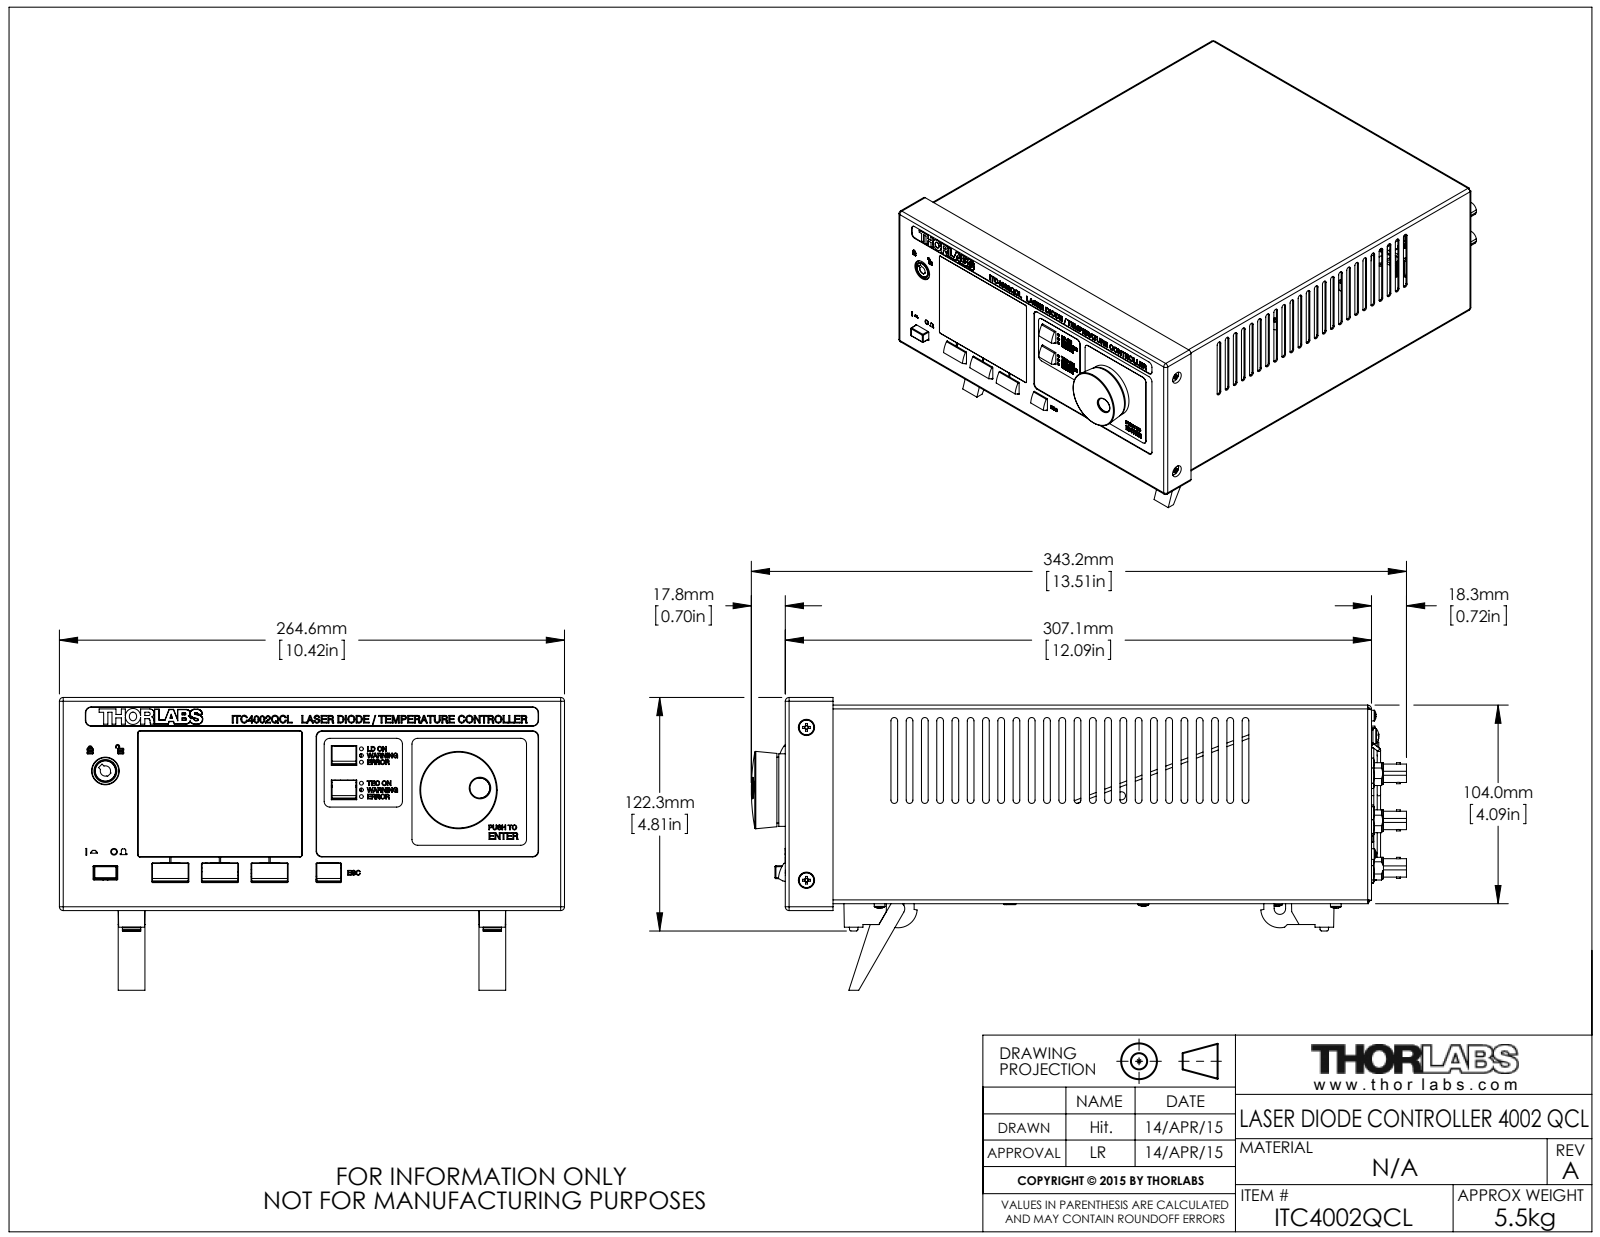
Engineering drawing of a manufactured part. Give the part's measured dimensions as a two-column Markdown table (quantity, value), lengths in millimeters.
| quantity | value |
| --- | --- |
| part name | MTN004957-E0W |
| STEP written by | SolidWorks 2014 (AUTOMOTIVE_DESIGN) |
| units | millimeters |
| bodies | 113 solids, 14390 faces (8699 planar, 2452 cylindrical, 3239 other) |
| overall size | 343.22 × 264.6 × 153.33 |
| volume | 734 865 mm³ |
| surface area | 897 095 mm² |
| round holes (diameter × count) | 2.5 × 37, 5.4 × 27, 1 × 25, 1.1 × 25, 3 × 18, 5.39 × 17, 3.5 × 12, 4.25 × 11, 2.01 × 10, 2.7 × 10, 3.1 × 8, 12 × 8 |
| round bosses / shafts (diameter × count) | 0.96 × 40, 1.8 × 20, 5.12 × 17, 3.56 × 16, 0.56 × 15, 0.71 × 14, 4 × 12, 3 × 12 |
| partial cylindrical surfaces (radius × count) | 1 × 92, 0.5 × 76, 0.76 × 48, 1.75 × 48, 0.7 × 47, 0.3 × 43, 1.02 × 36, 2 × 33 |
| main face-to-face distances | 1.5, 1, 103, 102, 100.5, 101.5, 254.6, 2.8, 1.8, 252.8 |
| hole center spacings | 19, 31.16, 49.5, 50.56, 70, 71.5, 24.7, 31.24 |
